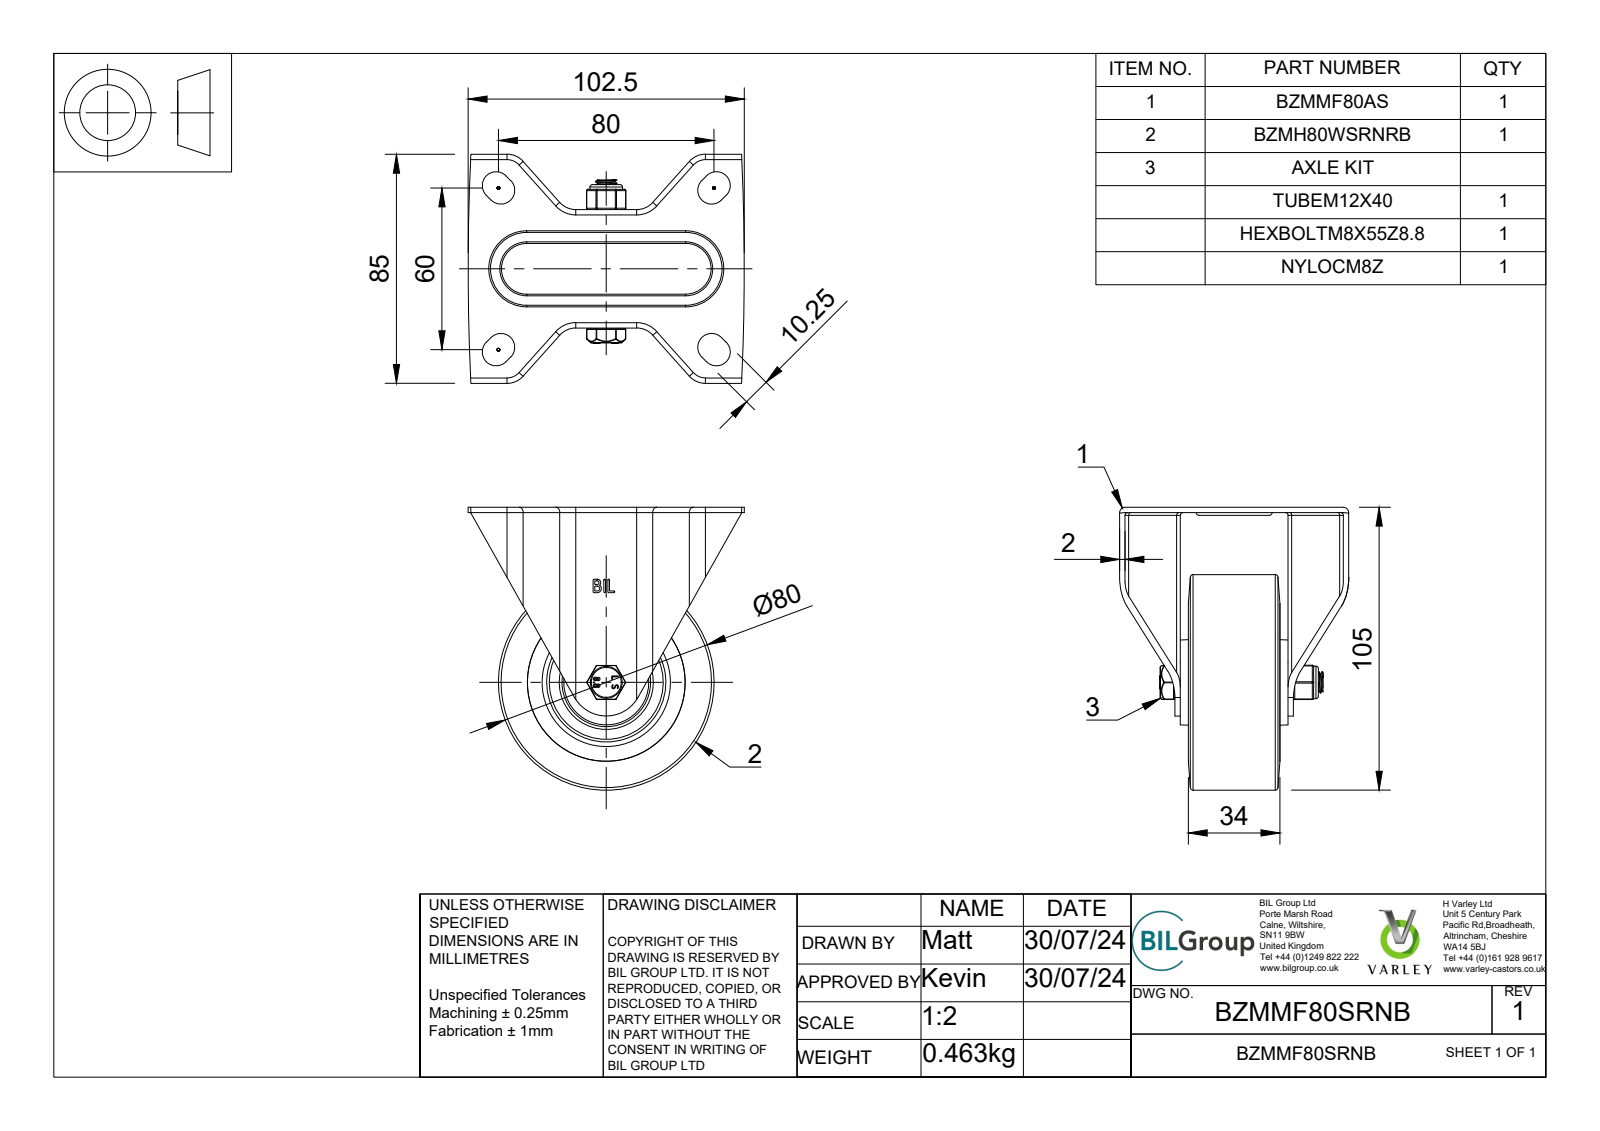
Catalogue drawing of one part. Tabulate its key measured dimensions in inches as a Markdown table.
| quantity | value |
| --- | --- |
| part name | BZMMF80SRNB v3; BZMMF80AS - 40 v2; ZINC PLATED, PRESSED STEEL BRACKET; BZMH80WSRNRB v1 (+6 more) |
| STEP written by | Autodesk Translation Framework v13.14.0.145 (AUTOMOTIVE_DESIGN) |
| units | inches |
| bodies | 17 solids, 488 faces (195 planar, 191 cylindrical, 102 other) |
| overall size | 4.134 × 4.035 × 3.346 |
| volume | 11.16 in³ |
| surface area | 135.4 in² |
| round holes (diameter × count) | 0.026 × 2, 0.315 × 1, 0.325 × 1, 0.331 × 1, 0.339 × 1, 0.492 × 1, 0.496 × 1, 0.807 × 1, 0.976 × 1, 2.303 × 1 |
| round bosses / shafts (diameter × count) | 0.148 × 8, 3.15 × 1, 0.969 × 1, 0.787 × 1, 0.476 × 1, 0.469 × 1, 0.453 × 1, 0.31 × 1 |
| partial cylindrical surfaces (radius × count) | 0.02 × 18, 0.01 × 12, 0.039 × 12, 0.079 × 8, 0.157 × 8, 0.202 × 8, 0.315 × 8, 0.013 × 4 |
| main face-to-face distances | 0.079, 0.203, 1.654, 1.575, 0.124, 0.118, 0.197, 0.282, 1.535, 1.457 |
| hole center spacings | 0.127, 0.098 |
